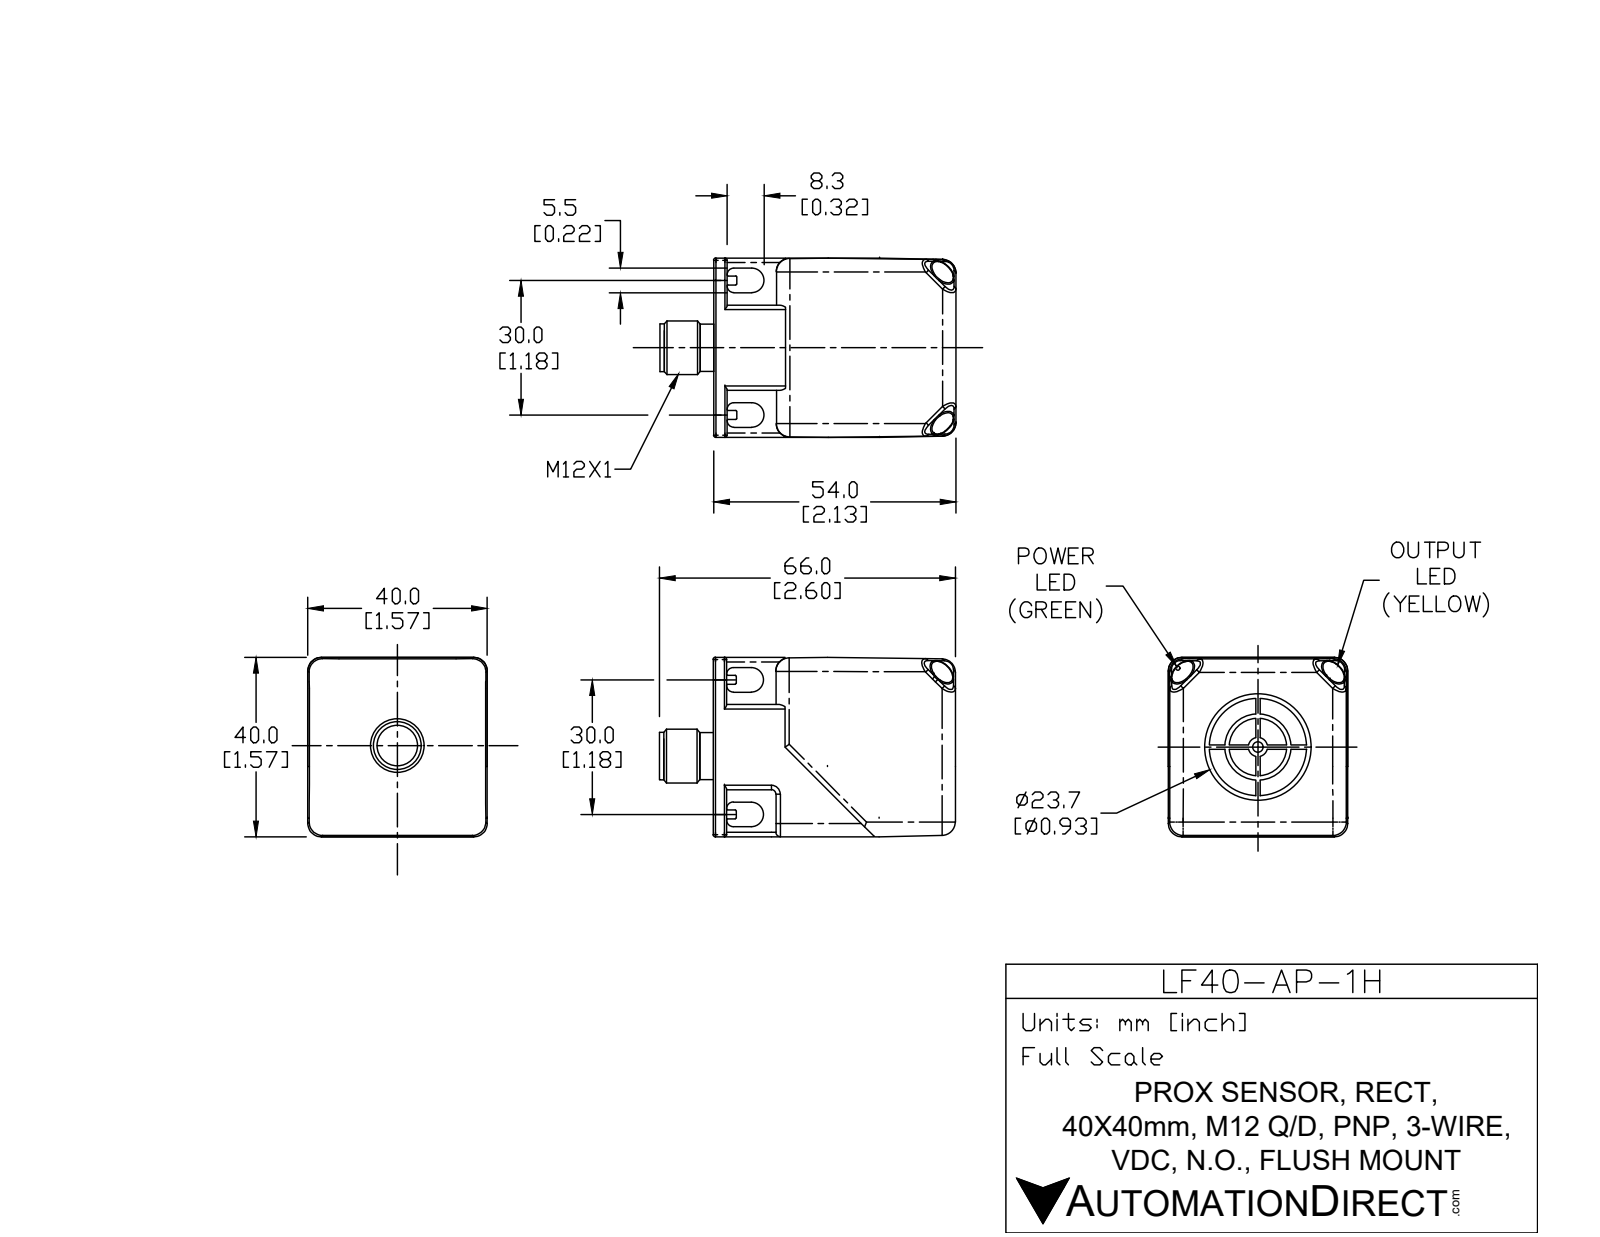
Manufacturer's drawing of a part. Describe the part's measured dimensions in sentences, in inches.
The part is named "LF40-AP-1H". Its 3-D file was written by "SolidWorks 2017 (AUTOMOTIVE_DESIGN)". It is 1 solid with 222 faces: 110 planar, 99 cylindrical and 13 other. Overall it measures 2.598 by 1.575 by 1.575 inches. Its volume is 4.765 cubic inches and its surface area 23.34 square inches. Round holes: 1 of diameter 0.331, 1 of diameter 0.362, 1 of diameter 0.583, 1 of diameter 0.933. Round bosses or shafts: 1 of diameter 0.854, 1 of diameter 0.504, 1 of diameter 0.472, 1 of diameter 0.417, 1 of diameter 0.413, 1 of diameter 0.354, 1 of diameter 0.276, 1 of diameter 0.091. Partial cylindrical surfaces (rounded edges, fillets, slot ends): 16 of radius 0.008, 10 of radius 0.039, 10 of radius 0.118, 8 of radius 0.059, 4 of radius 0.02, 4 of radius 0.108, 4 of radius 0.197, 1 of radius 0.024. The main face-to-face distances are 1.575, 2.126, 0.413, 1.161, 1.181, 0.118, 2.008, 0.325, 0.089, 0.305. The hole center spacings are 0.079.
